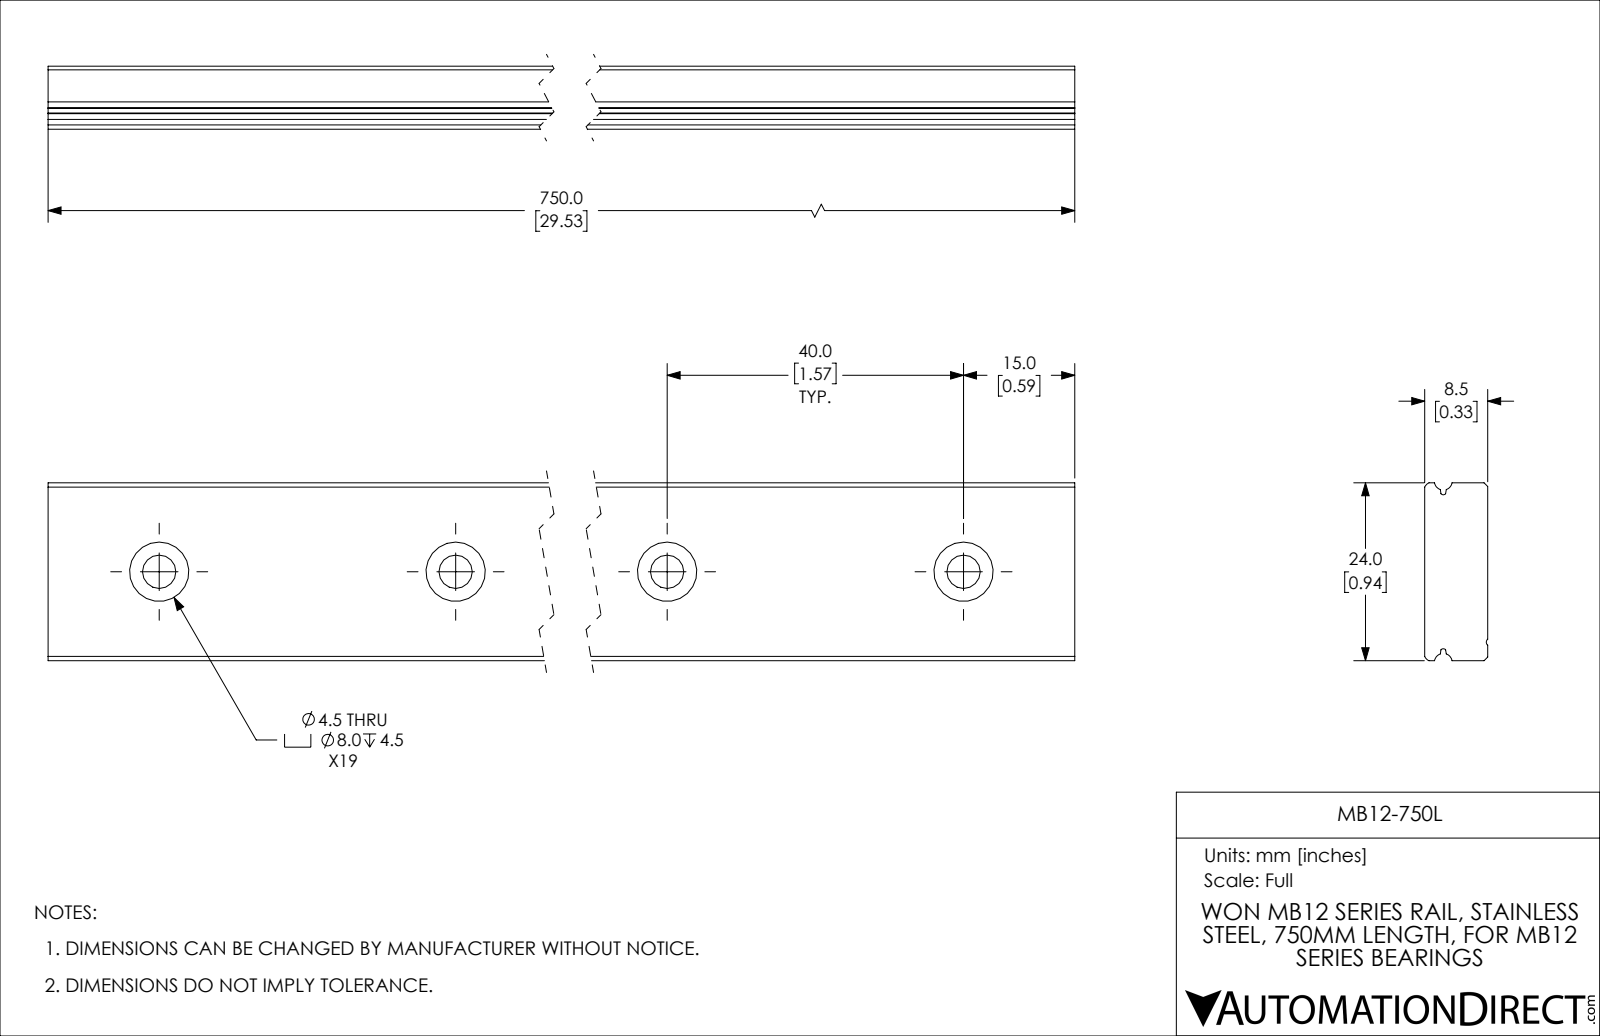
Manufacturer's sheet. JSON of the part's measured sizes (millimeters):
{"part_name": "MB12-750L", "step_written_by": "SolidWorks 2019 (CONFIG_CONTROL_DESIGN)", "units": "millimeters", "bodies": {"solids": 1, "faces": 120, "planar": 34, "cylindrical": 86, "other": 0}, "overall_size": [750, 24, 8.5], "volume_mm3": 143764, "surface_area_mm2": 53964, "round_holes": [[4.5, 19], [8, 19]], "partial_cylinders_radius": [[0.42, 2], [1.15, 2], [1.2, 2], [0.5, 1]], "face_to_face_distances": [8.5, 24, 2.21, 4, 4.5, 750], "hole_center_spacings": [40, 80, 120, 160, 200, 240, 280, 320]}
